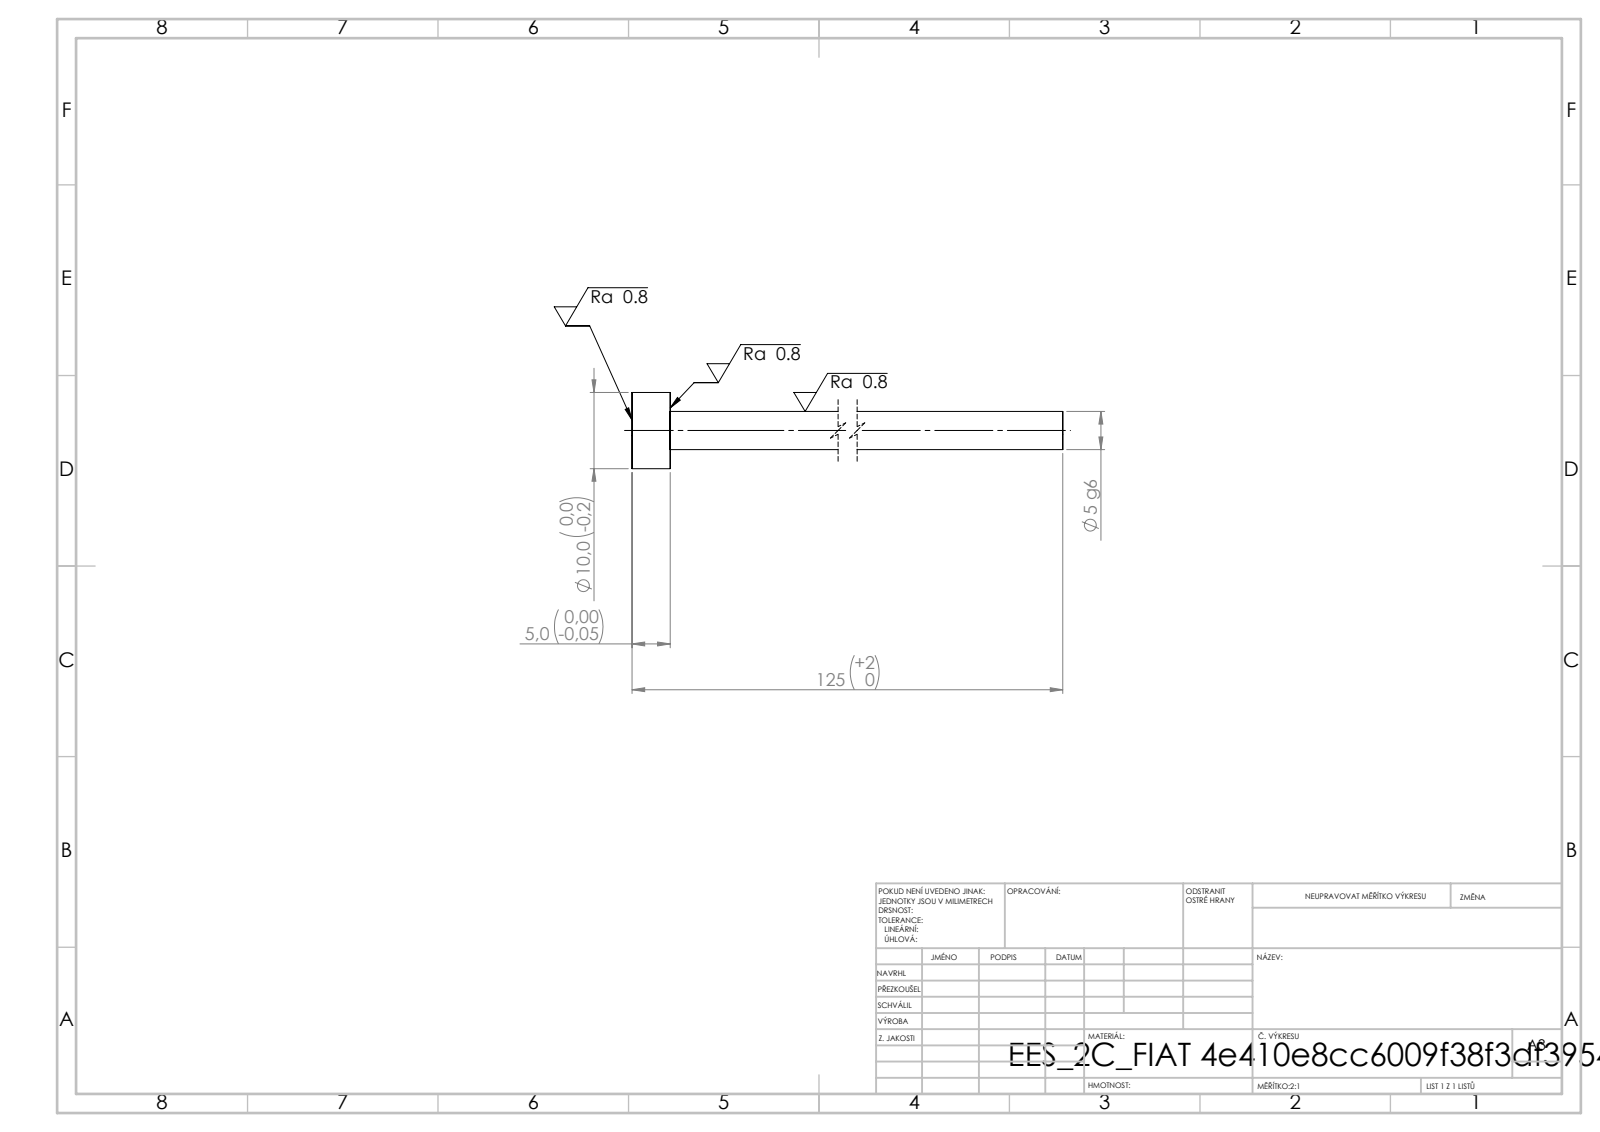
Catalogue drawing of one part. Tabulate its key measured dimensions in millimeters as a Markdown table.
| quantity | value |
| --- | --- |
| STEP written by | SolidWorks 2019 (CONFIG_CONTROL_DESIGN) |
| units | millimeters |
| bodies | 1 solid, 7 faces (3 planar, 4 cylindrical, 0 other) |
| overall size | 125 × 10 × 10 |
| volume | 2 749 mm³ |
| surface area | 2 199 mm² |
| round bosses / shafts (diameter × count) | 10 × 1, 5 × 1 |
| main face-to-face distances | 5, 125, 120 |
